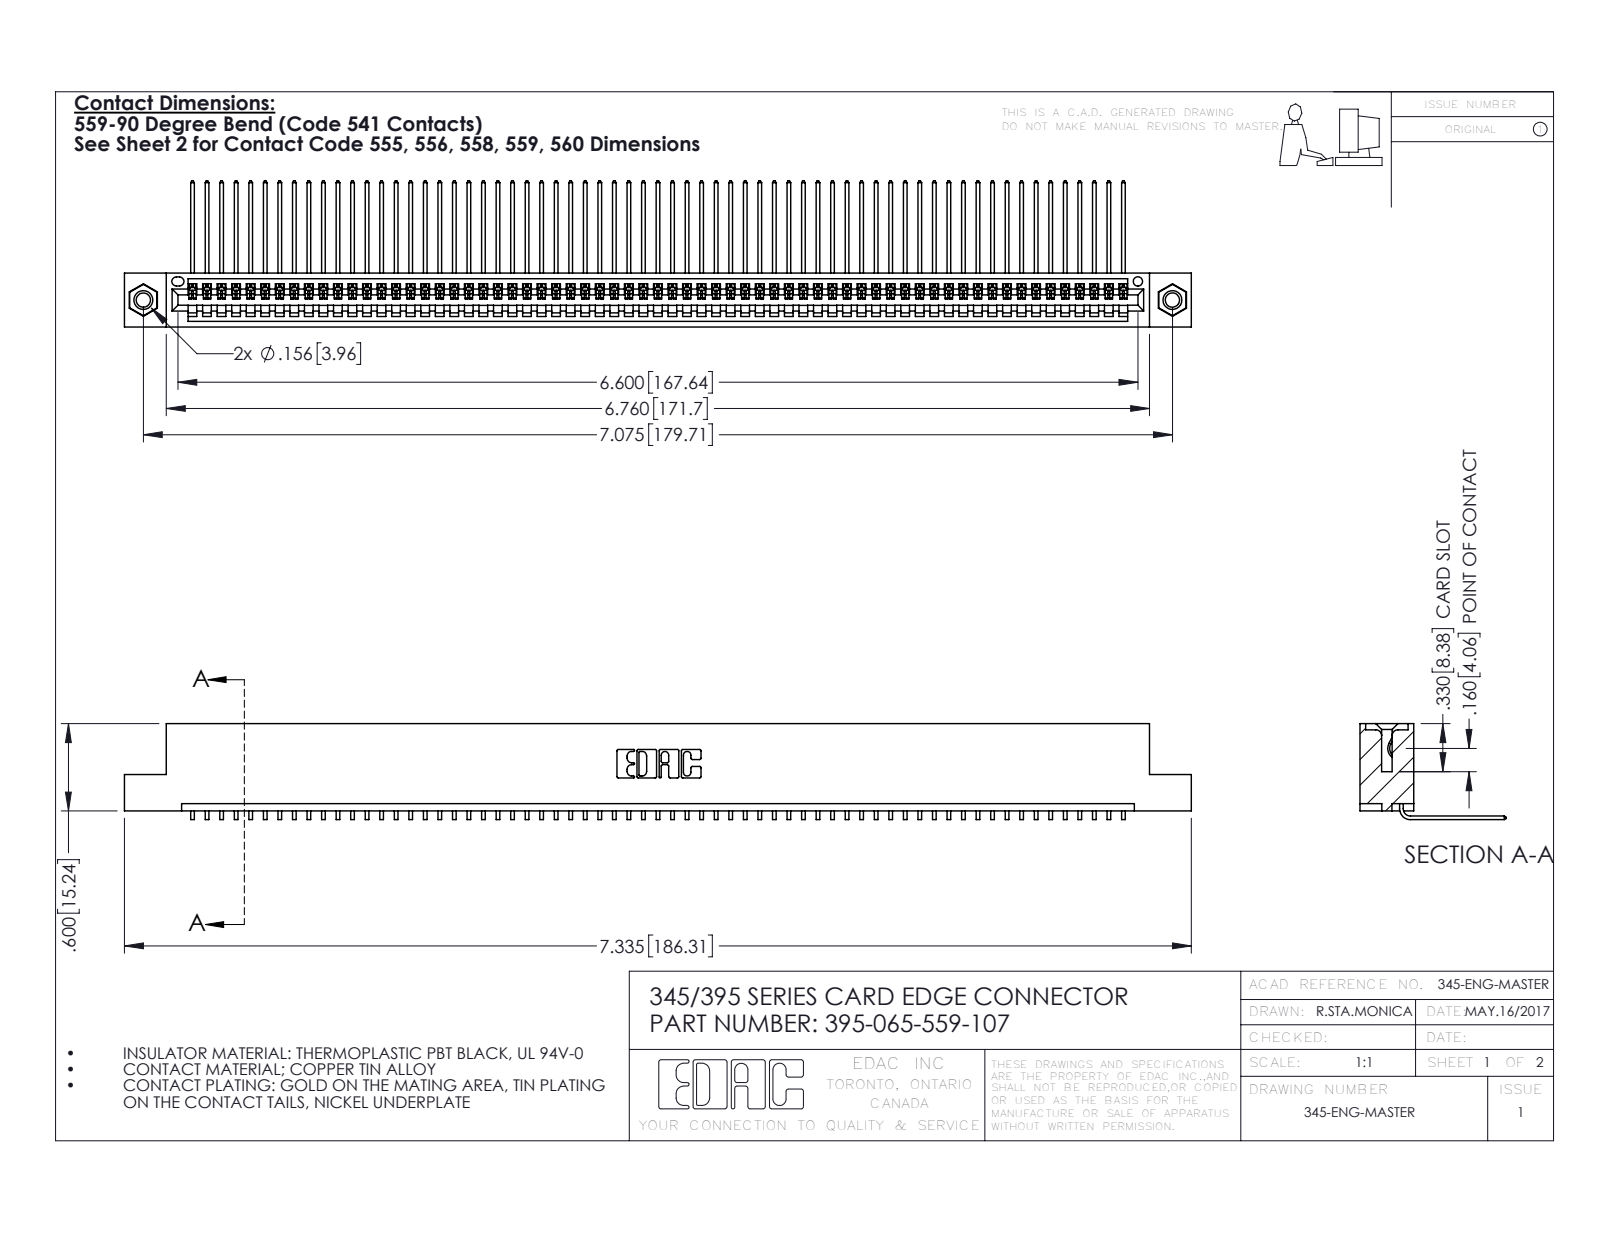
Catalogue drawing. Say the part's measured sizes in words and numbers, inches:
The part is named "345-250-001_345-250-005-103; 345 Part_Flush Mounting Lugs - 0.156 Dia-TI; 345-292-001_558 559 Tail - 1; 395-065-559-107". Its 3-D file was written by "SolidWorks 2016 (CONFIG_CONTROL_DESIGN)". It is 68 solids with 4086 faces: 2842 planar, 1228 cylindrical and 16 other. Overall it measures 7.335 by 1.005 by 0.659 inches. Its volume is 1.104 cubic inches and its surface area 39.76 square inches. Round holes: 2 of diameter 0.098, 2 of diameter 0.125, 2 of diameter 0.156, 1 of diameter 0.064. Round bosses or shafts: 2 of diameter 0.155. Partial cylindrical surfaces (rounded edges, fillets, slot ends): 130 of radius 0.006, 22 of radius 0.01, 6 of radius 0.007, 6 of radius 0.031, 3 of radius 0.026, 2 of radius 0.031, 2 of radius 0.04, 1 of radius 0.014. The main face-to-face distances are 0.072, 0.298, 0.37, 0.2, 0.098, 0.272, 0.025, 0.225, 0.149, 0.072. The hole center spacings are 0.27, 6.839, 7.075.
